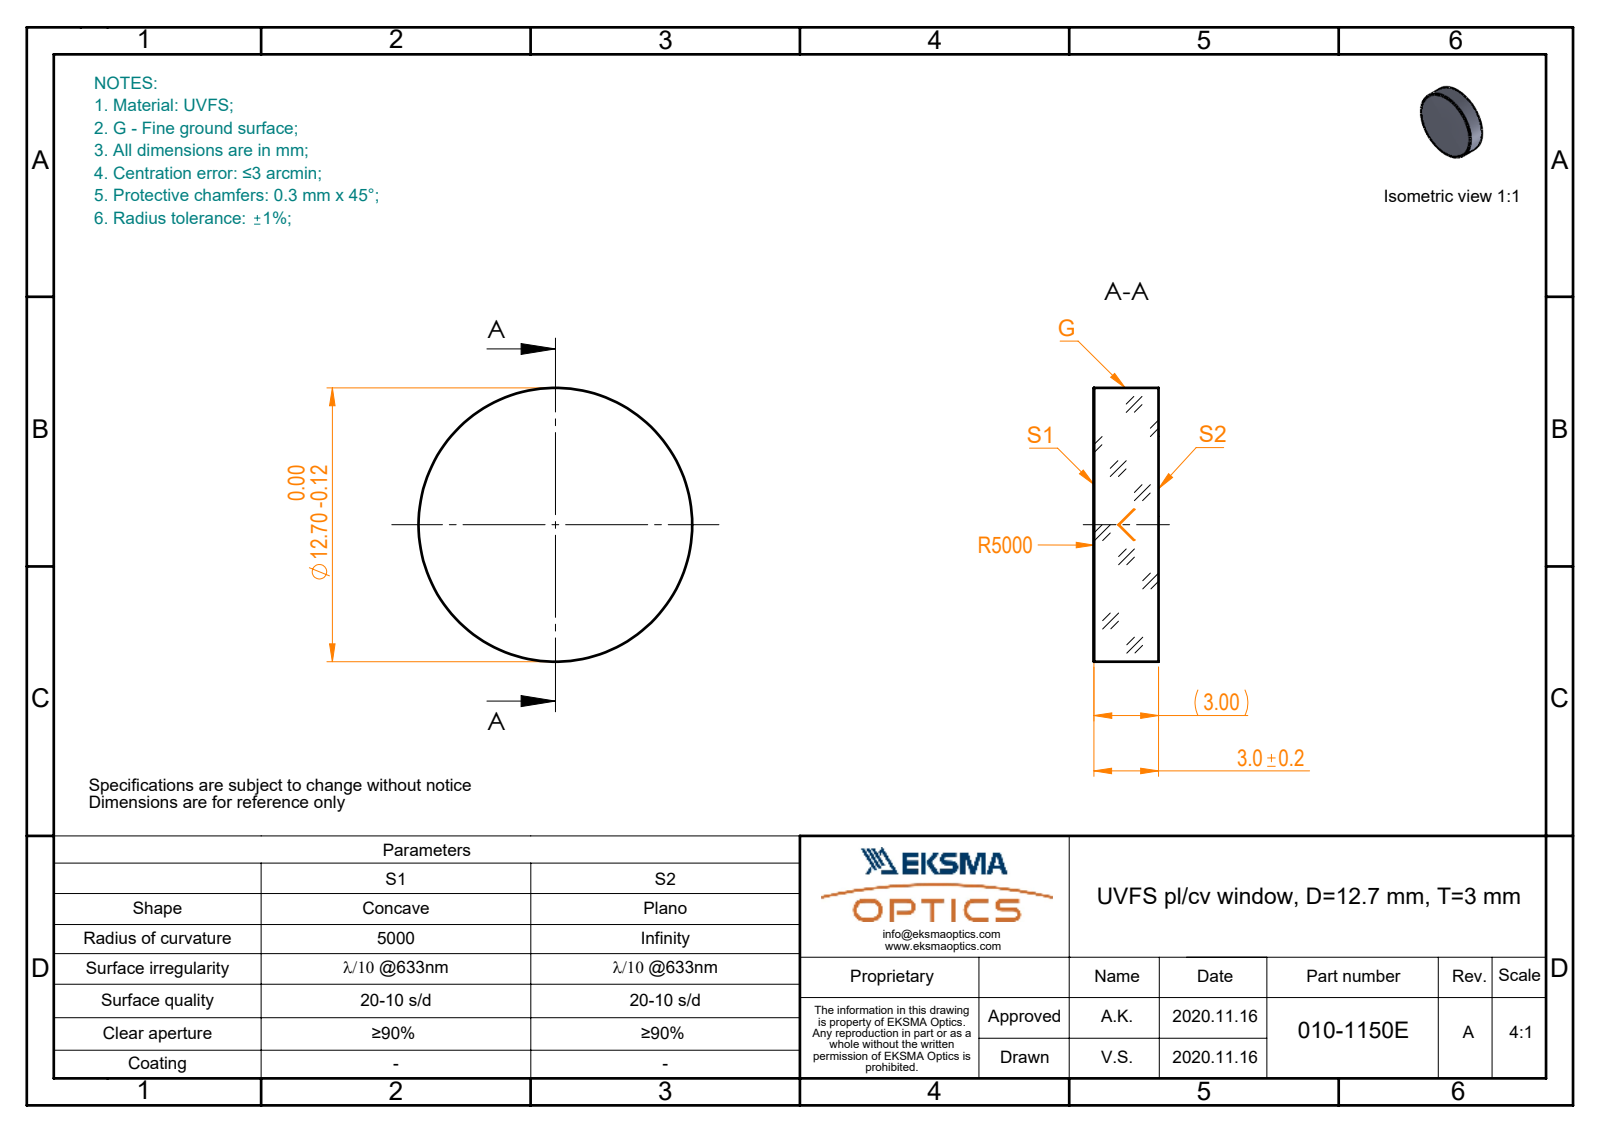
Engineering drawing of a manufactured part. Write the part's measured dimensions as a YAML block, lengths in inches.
part_name: "010-1150E_UVFS_PCV_window"
step_written_by: "SolidWorks 2019 (CONFIG_CONTROL_DESIGN)"
units: inches
bodies: {solids: 1, faces: 5, planar: 1, cylindrical: 2, other: 2}
overall_size: [0.5, 0.5, 0.118]
volume: 0.023
surface_area: 0.578
round_bosses_or_shafts:
  - {diameter: 0.5, count: 1}
